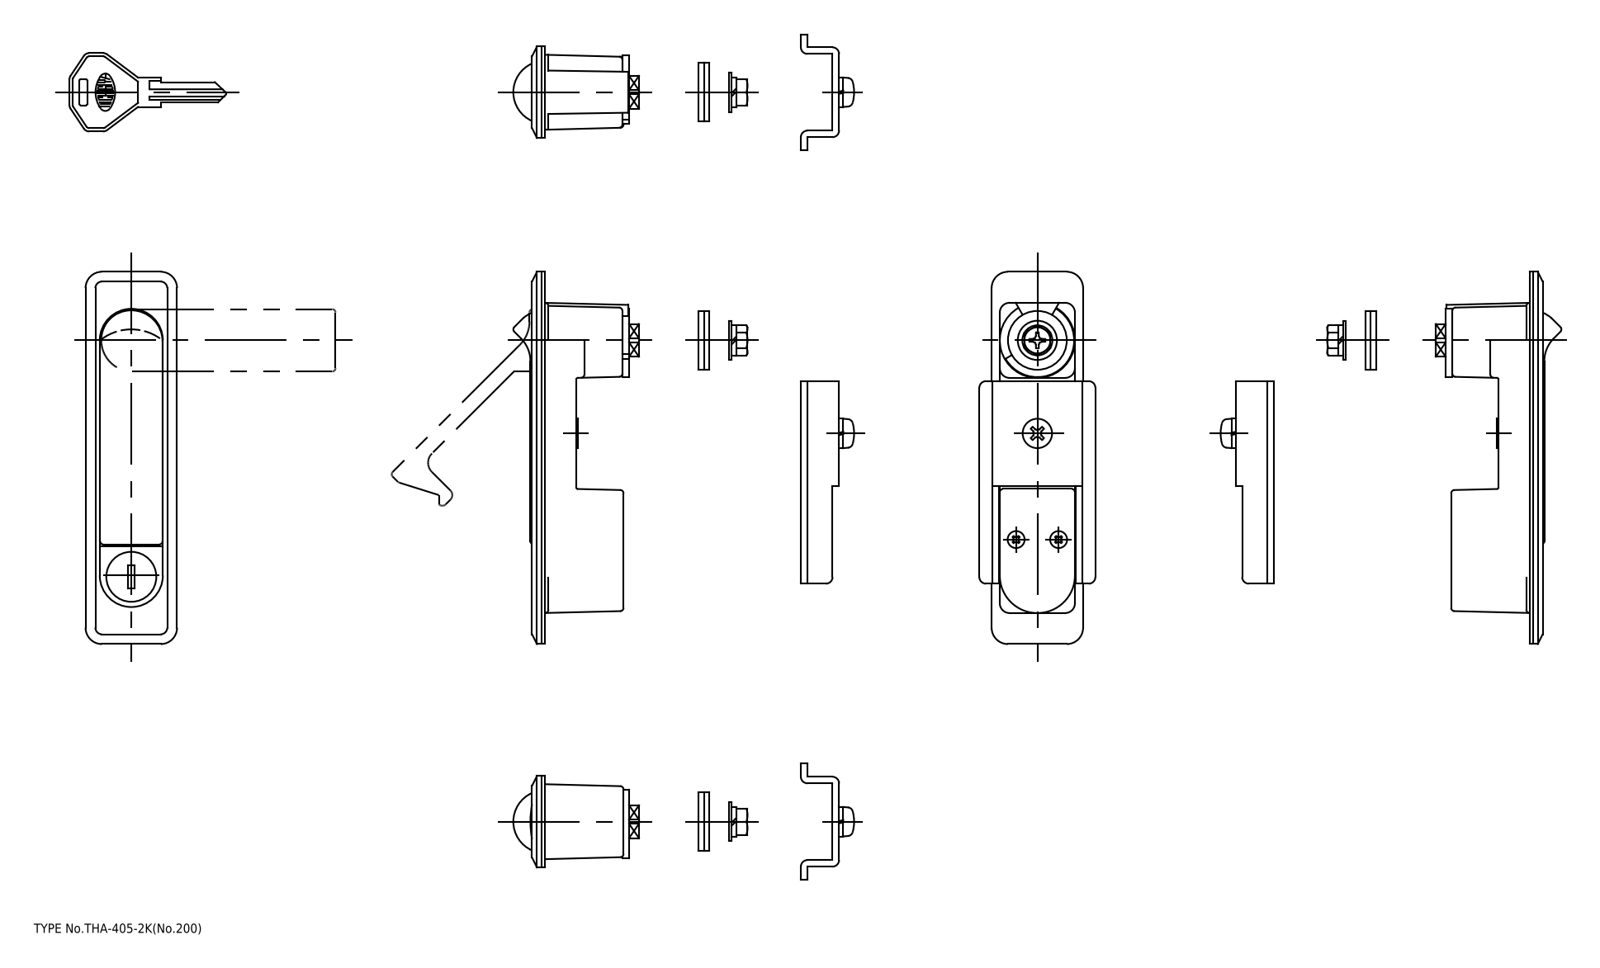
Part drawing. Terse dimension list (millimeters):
name: 67131285; 67131298; 67131311; 67131324 (+8 more)
written by: CADfix (AUTOMOTIVE_DESIGN)
unit: mm
bodies: 12 solids, 480 faces (0 planar, 0 cylindrical, 480 other)
size: 114 × 103.8 × 35.5
volume: 45 843 mm³; area: 38 109 mm²
